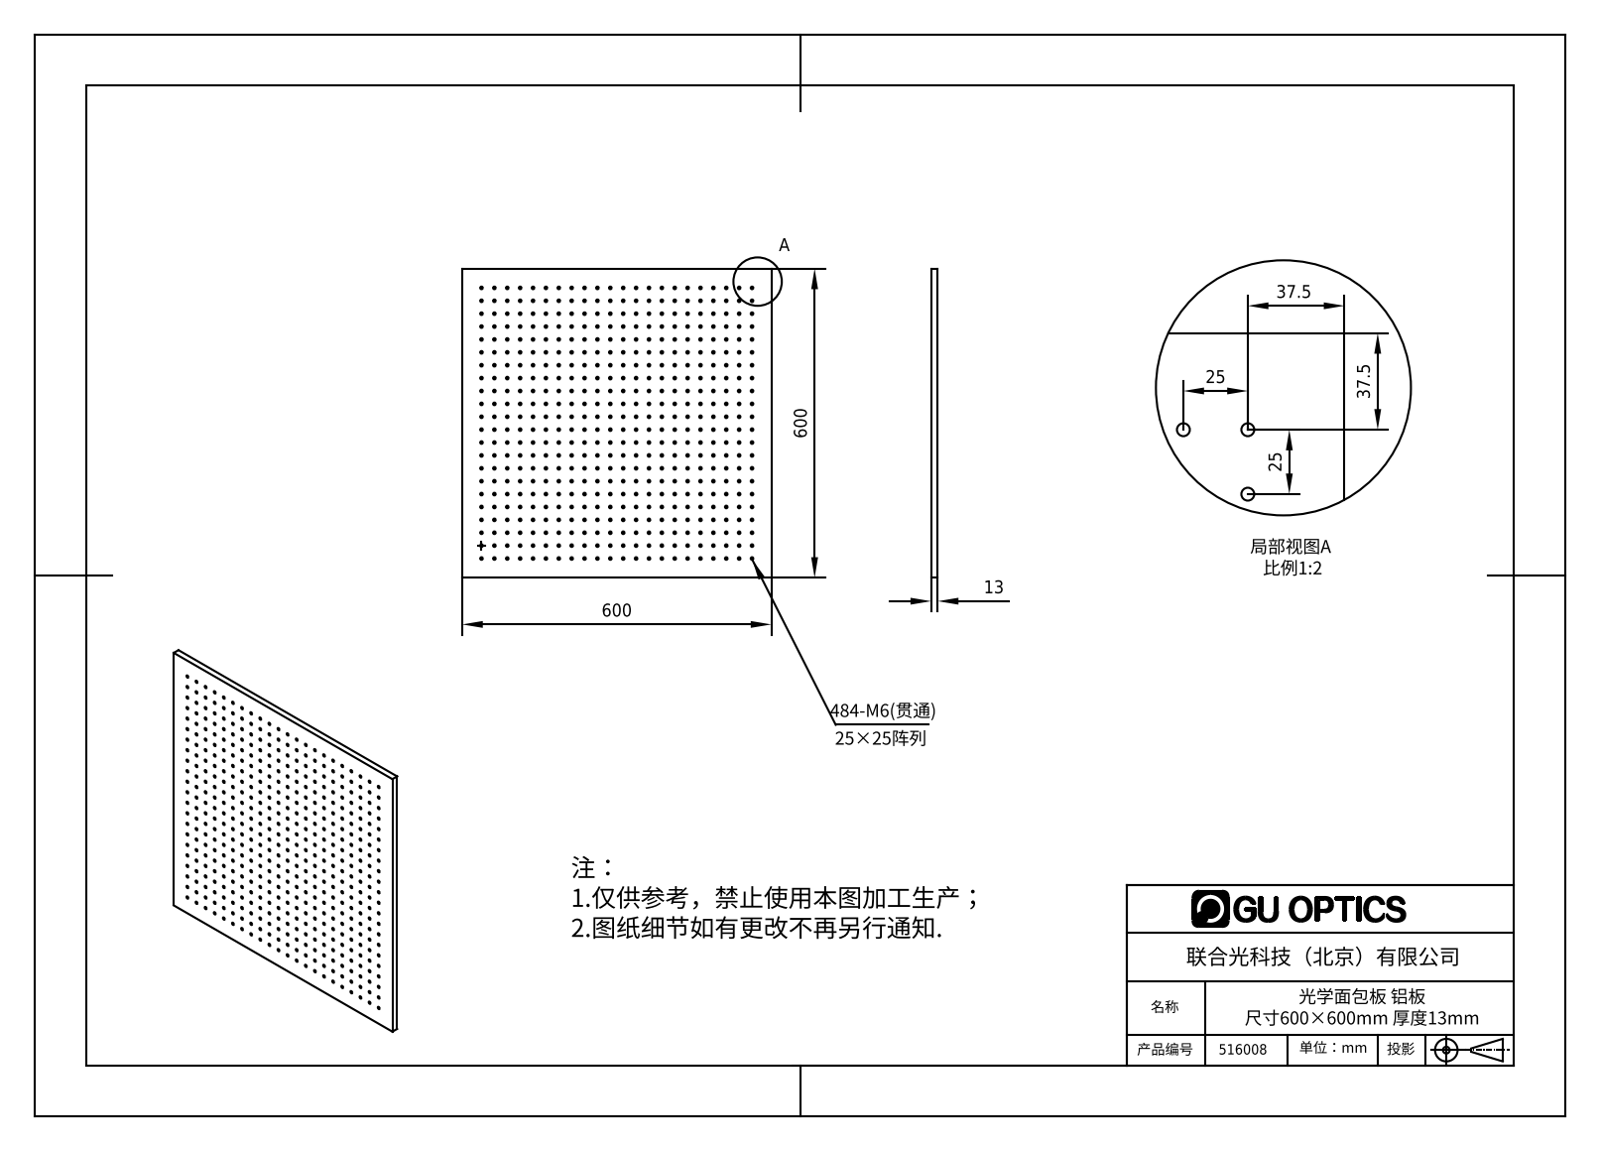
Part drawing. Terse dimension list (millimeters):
name: 516008
written by: SolidWorks 2016 (AUTOMOTIVE_DESIGN)
unit: mm
bodies: 1 solid, 974 faces (6 planar, 968 cylindrical, 0 other)
size: 600 × 600 × 13
volume: 4 556 000 mm³; area: 831 028 mm²
holes: 484× ⌀5
face distances: 13, 600
hole spacings: 25, 50, 75, 100, 55.9, 125, 35.36, 150
